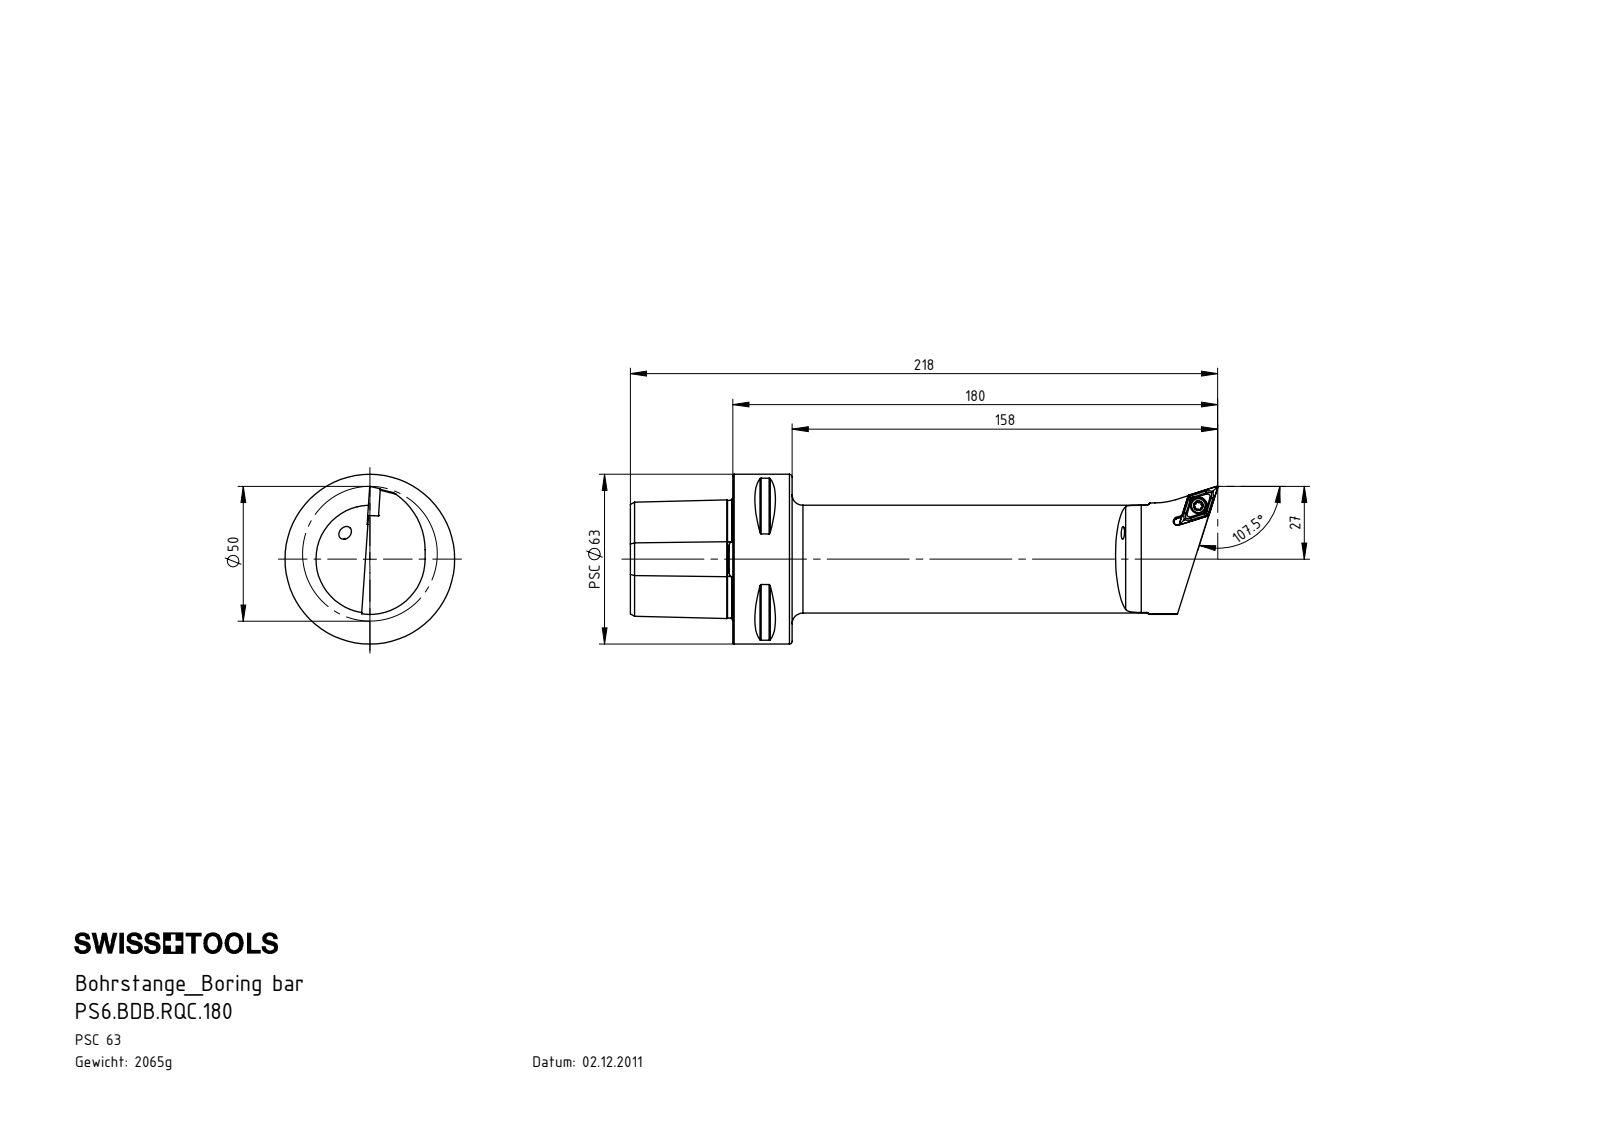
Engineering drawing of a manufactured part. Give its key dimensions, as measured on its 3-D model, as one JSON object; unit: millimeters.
{"part_name": "PS6-BDB.RQC.180; KVT_MB_600_050; WCB-ER2.001.009_A; PS6-BDB.RQC.180_A (+1 more)", "step_written_by": "SolidWorks 2012 (CONFIG_CONTROL_DESIGN)", "units": "millimeters", "bodies": {"solids": 5, "faces": 287, "planar": 53, "cylindrical": 74, "other": 160}, "overall_size": [218, 63, 63], "volume_mm3": 262641, "surface_area_mm2": 42659, "round_holes": [[4, 2], [4.2, 2], [3.3, 1], [4.4, 1], [6.1, 1], [8.1, 1], [8.5, 1], [18, 1], [28, 1], [32, 1]], "round_bosses_or_shafts": [[63, 1], [40, 1], [5.25, 1], [5, 1], [4, 1]], "partial_cylinders_radius": [[0.5, 8], [0.34, 6], [0.59, 6], [1.25, 1], [3, 1], [6, 1], [20.5, 1], [25, 1]], "face_to_face_distances": [22, 38, 60, 24.88, 27, 11, 33, 55.8, 3.66, 37.8], "hole_center_spacings": [27.5]}
